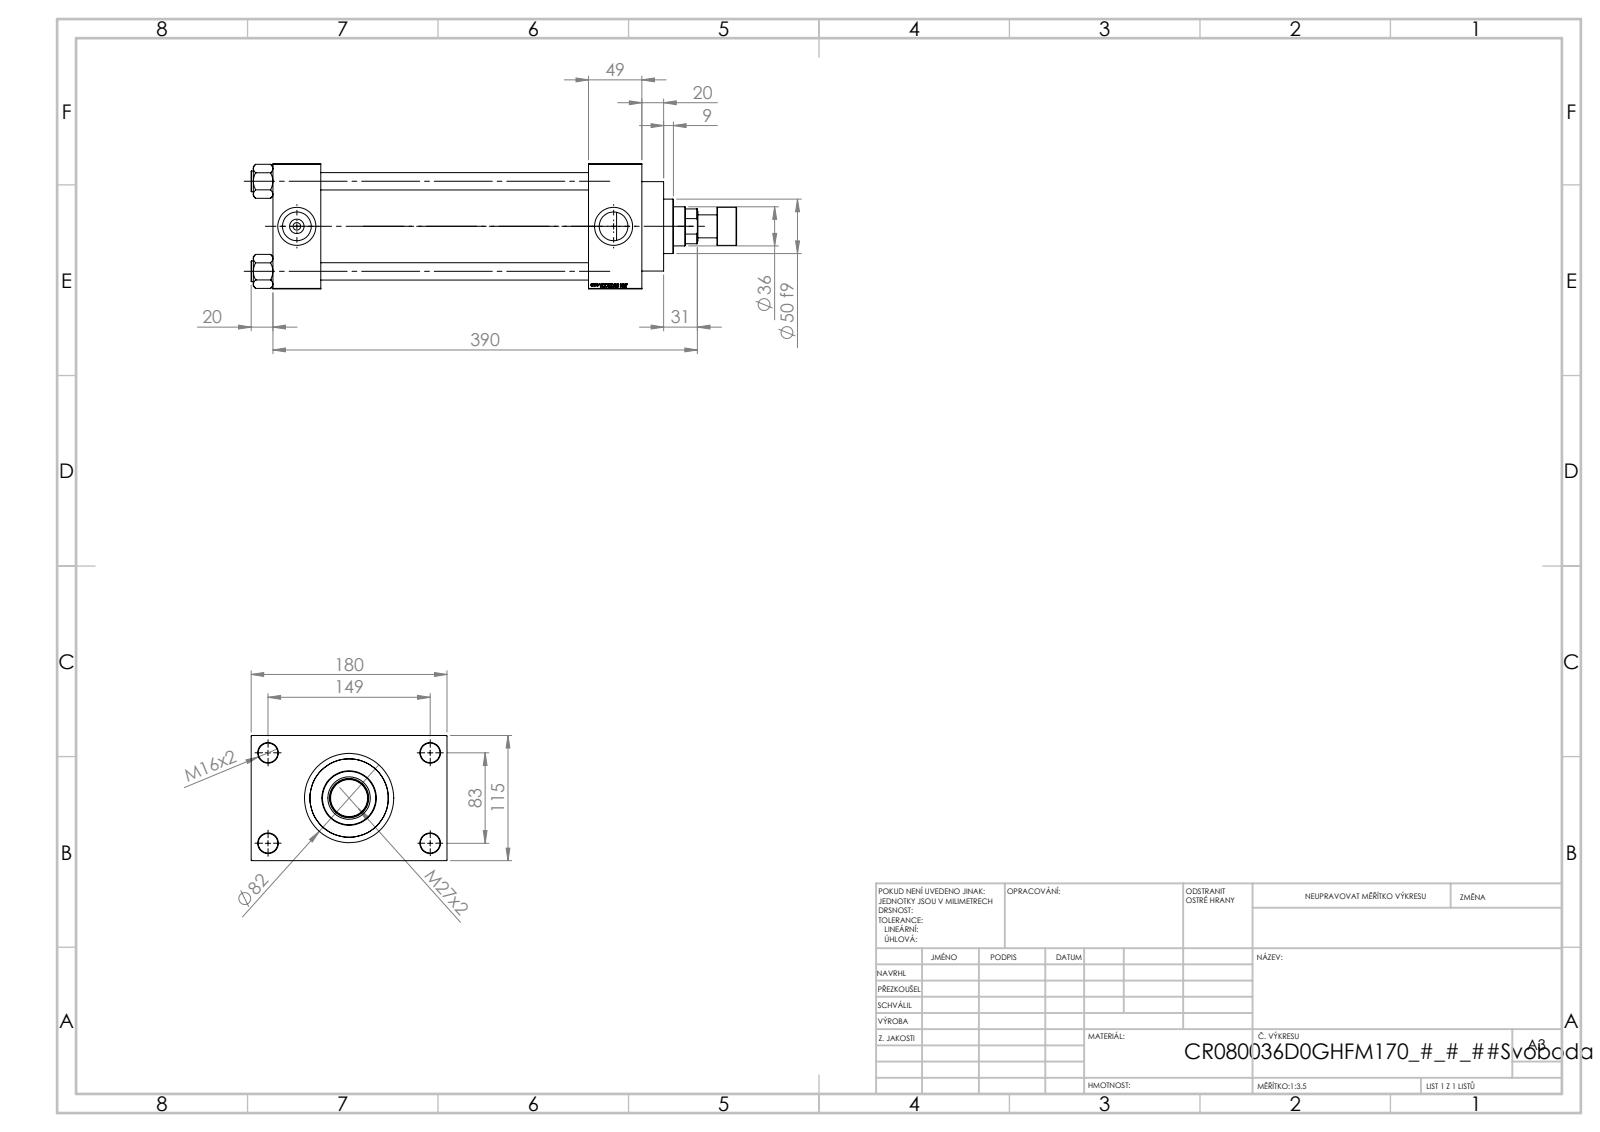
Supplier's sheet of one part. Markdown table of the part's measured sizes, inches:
| quantity | value |
| --- | --- |
| part name | V215CR_D_Body; V215CR_VCP_D; V215CR_ROD_END_F; NUT_M5_D (+2 more) |
| STEP written by | SolidWorks 2019 (CONFIG_CONTROL_DESIGN) |
| units | inches |
| bodies | 12 solids, 1165 faces (549 planar, 92 cylindrical, 524 other) |
| overall size | 17.559 × 7.087 × 4.528 |
| volume | 150.9 in³ |
| surface area | 701.5 in² |
| round holes (diameter × count) | 0.63 × 4, 0.709 × 4, 0.276 × 2, 1.041 × 2, 1.378 × 2, 1.004 × 1, 1.417 × 1, 1.535 × 1, 2.402 × 1, 2.835 × 1, 3.15 × 1 |
| round bosses / shafts (diameter × count) | 0.748 × 4, 3.386 × 1, 3.228 × 1, 1.969 × 1, 1.378 × 1, 0.827 × 1 |
| main face-to-face distances | 4.528, 9.685, 1.929, 11.614, 1.732, 11.417, 13.346, 1.28, 5.807, 7.087 |
| hole center spacings | 1.305, 2.302, 3.256, 3.357, 3.513, 4.561, 5.607, 3.268 |
